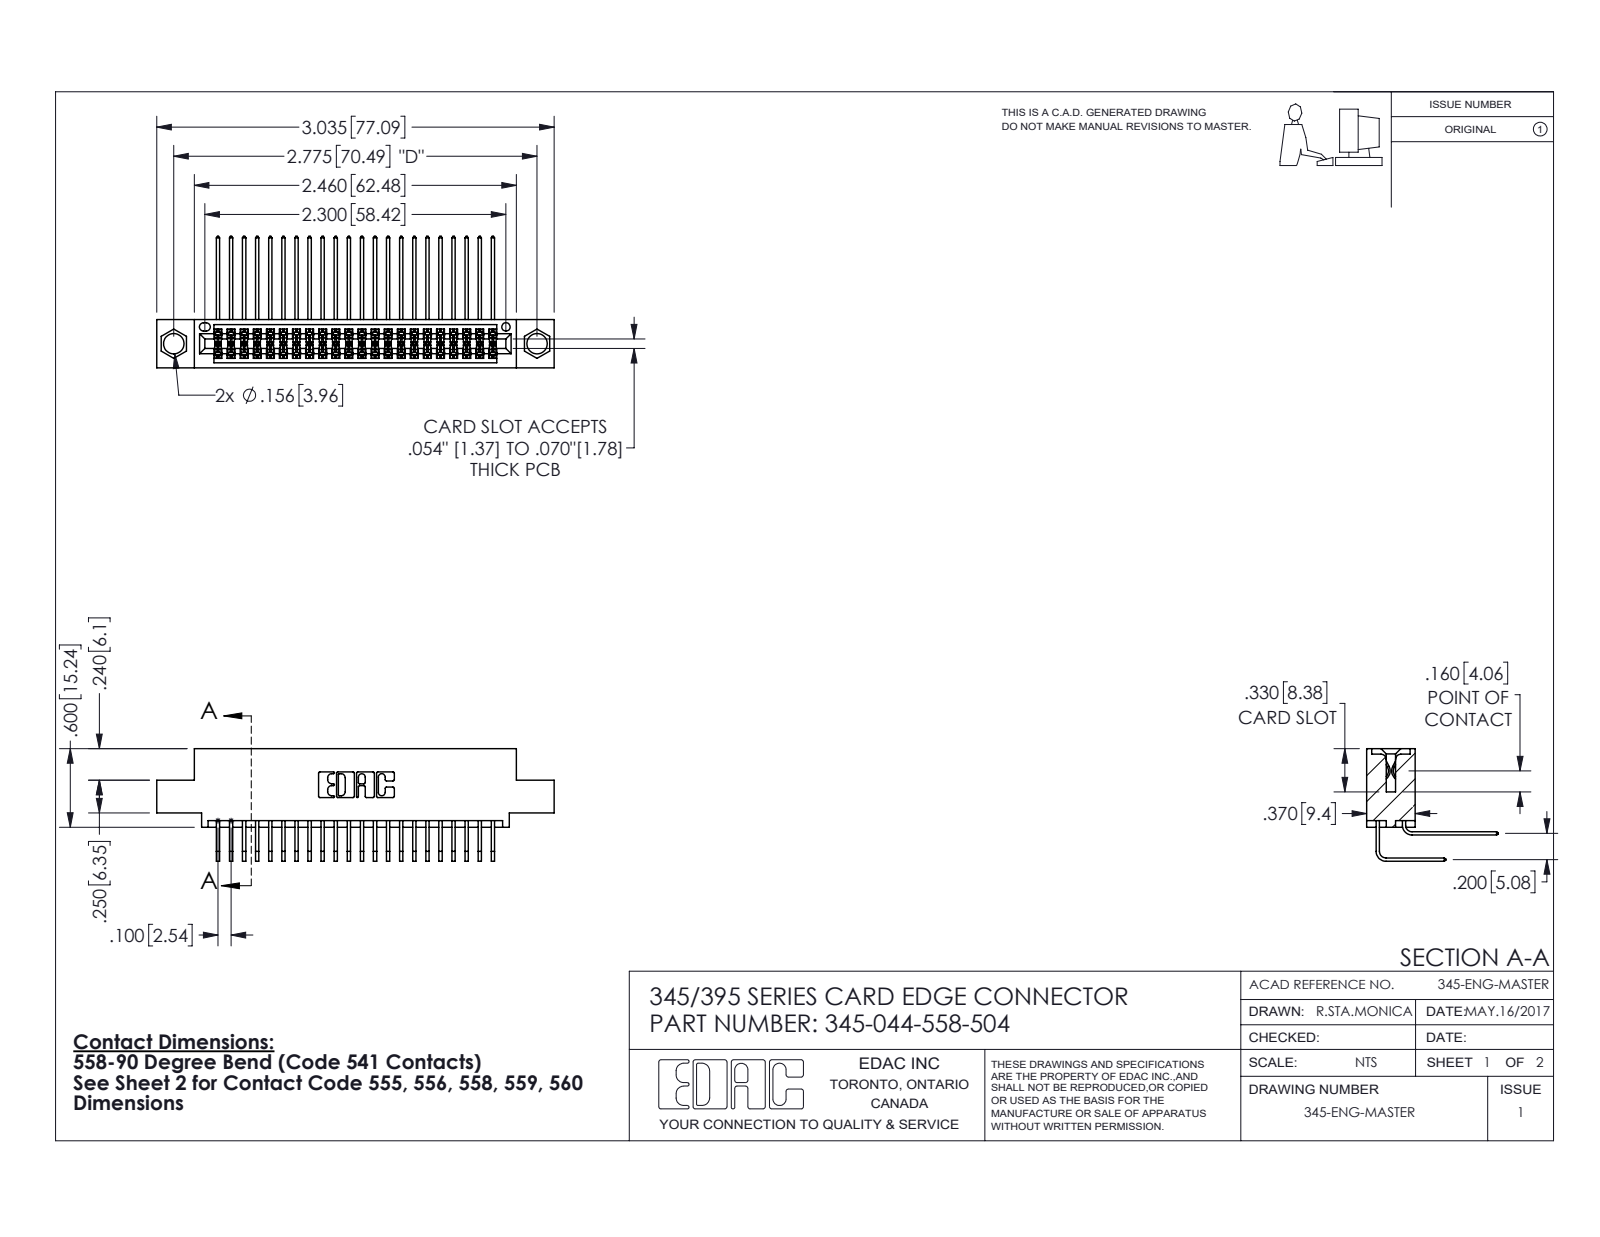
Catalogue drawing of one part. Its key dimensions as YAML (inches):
part_name: "345-292-001_558 559 Tail - 1; 345 Part_0.110 Offset - 0.156 Dia-TI; 345-292-001_558 Tail - 2; 345-044-558-504"
step_written_by: "SolidWorks 2020 (CONFIG_CONTROL_DESIGN)"
units: inches
bodies: {solids: 45, faces: 2432, planar: 1638, cylindrical: 794, other: 0}
overall_size: [3.035, 1.005, 0.859]
volume: 0.45
surface_area: 18.07
round_holes:
  - {diameter: 0.156, count: 2}
  - {diameter: 0.064, count: 1}
partial_cylinders:
  - {radius: 0.006, count: 88}
  - {radius: 0.01, count: 22}
  - {radius: 0.007, count: 6}
  - {radius: 0.031, count: 6}
  - {radius: 0.026, count: 3}
  - {radius: 0.014, count: 2}
  - {radius: 0.019, count: 2}
  - {radius: 0.022, count: 2}
face_to_face_distances: [0.072, 0.298, 0.2, 0.37, 0.098, 0.272, 0.025, 0.225, 0.025, 0.175]
hole_center_spacings: [0.27, 2.541, 2.775]
